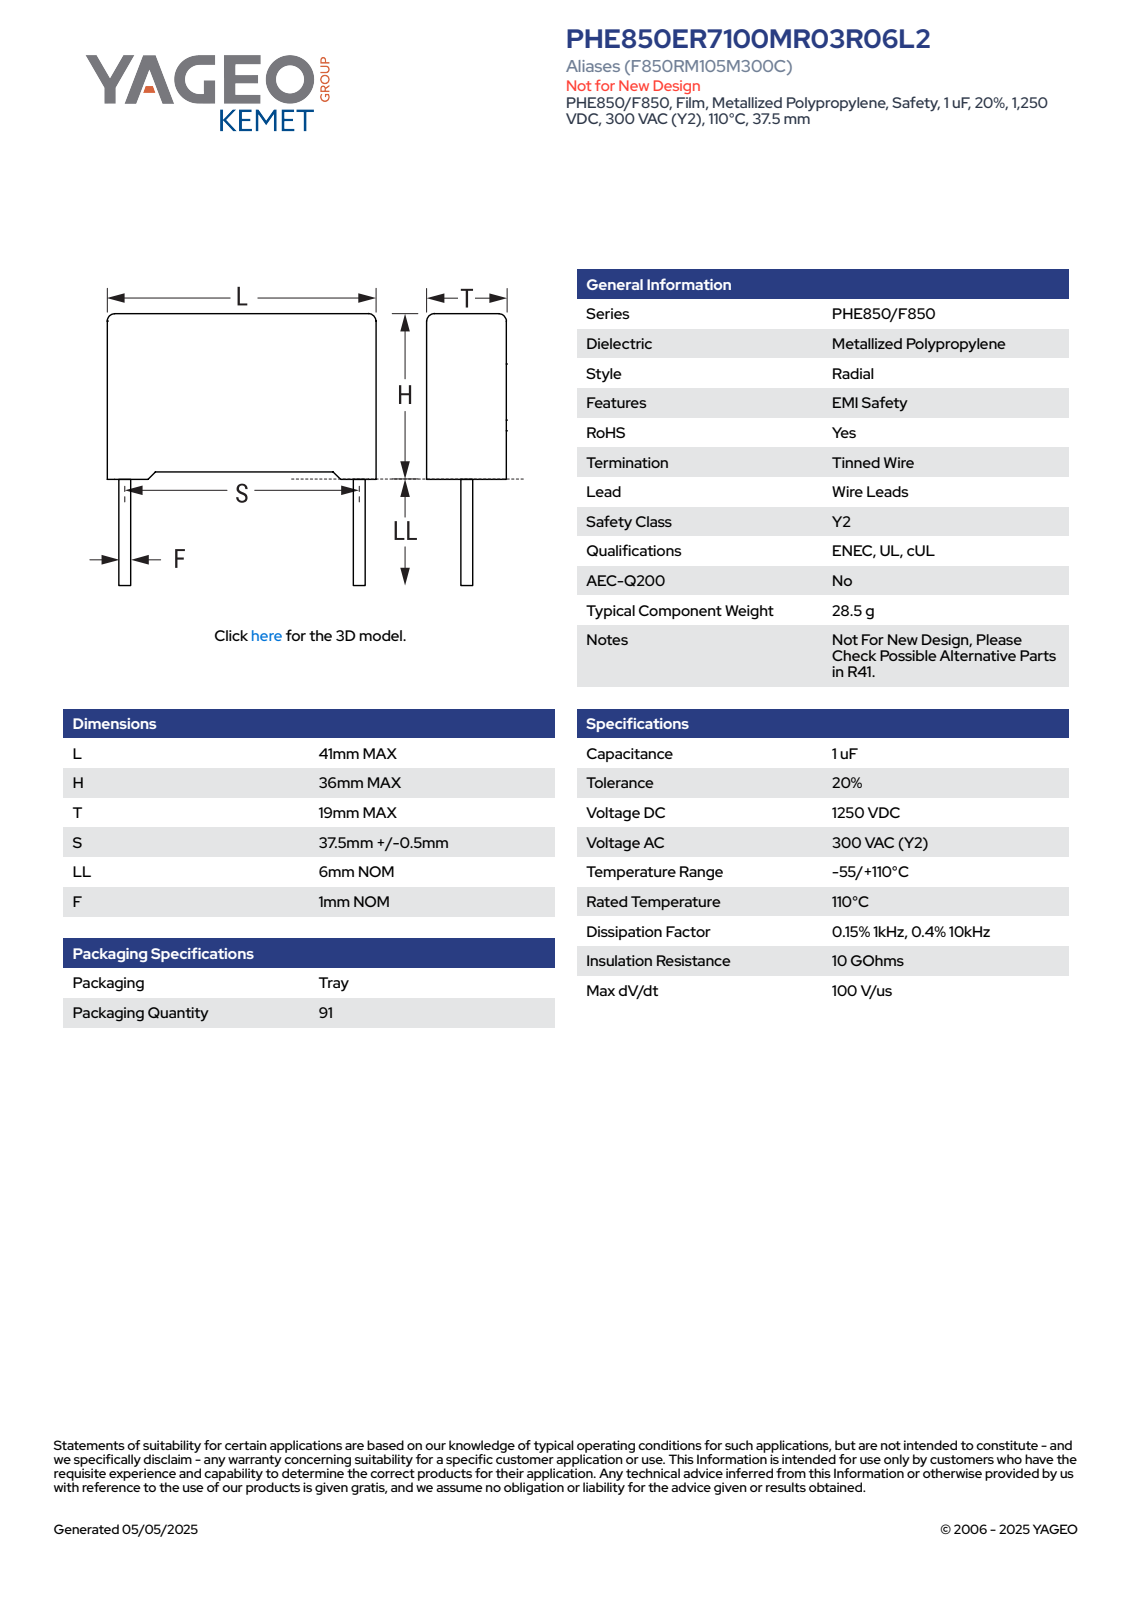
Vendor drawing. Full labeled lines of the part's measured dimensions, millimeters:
Part name (STEP PRODUCT): CFR_RB2_41X36X19_L41H36T19S37.5LL6F1
STEP written by: SolidWorks 2021 (AUTOMOTIVE_DESIGN)
Units: millimetres
Bodies: 4 solids, 87 faces (79 planar, 8 cylindrical, 0 other)
Overall size (bounding box): 42 × 41 × 19
Volume: 27 207 mm³ · Surface area: 5 977 mm²
Round bosses / shafts (diameter × count): ⌀1 ×2
Partial cylindrical surfaces — rounded edges, fillets, slot ends (radius × count): R0.5 ×4
Main face-to-face distances: 19, 41, 34.76, 0.49, 35.25, 0.75, 1.24, 36, 19.01, 1.37
